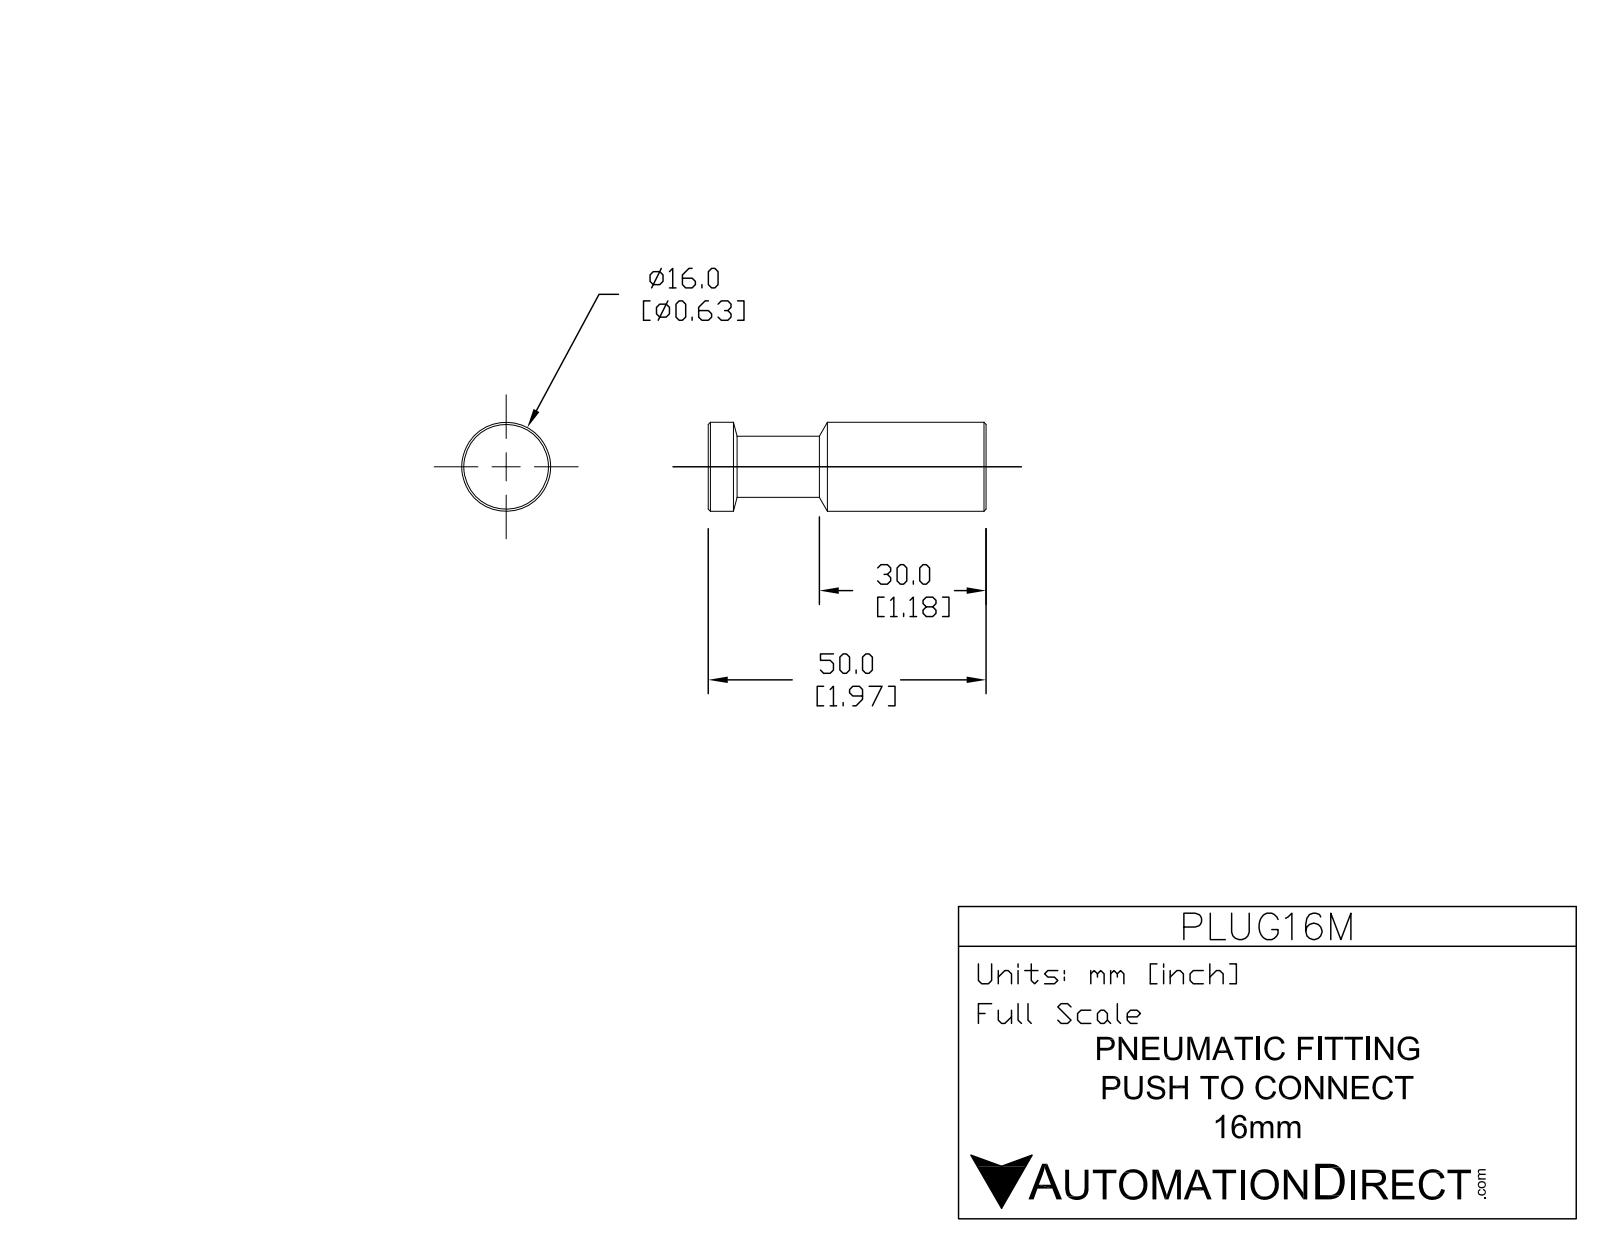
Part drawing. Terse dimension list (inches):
name: PLUG16M
written by: SolidWorks 2015 (AUTOMOTIVE_DESIGN)
unit: in
bodies: 1 solid, 16 faces (2 planar, 6 cylindrical, 8 other)
size: 1.969 × 0.63 × 0.63
volume: 0.509 in³; area: 4.318 in²
bosses: 1× ⌀0.63, 1× ⌀0.433
face distances: 1.969
